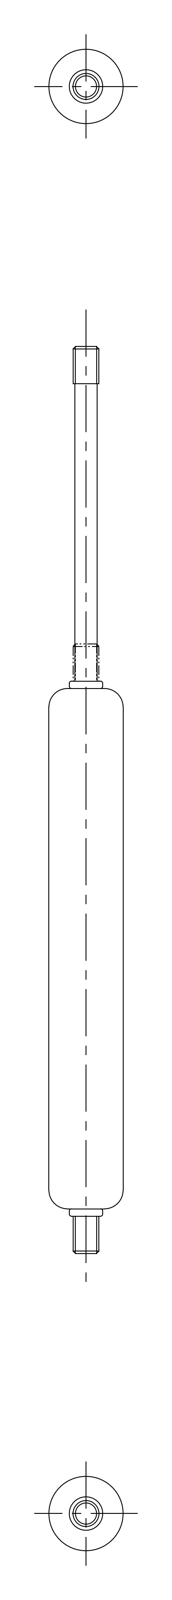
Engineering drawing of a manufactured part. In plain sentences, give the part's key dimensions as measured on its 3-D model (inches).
The part is named "rod; TM_277_40_80_29277_36". Its 3-D file was written by "CADfix (AUTOMOTIVE_DESIGN)". It is 2 solids with 36 faces: 0 planar, 0 cylindrical and 36 other. Overall it measures 4.803 by 0.394 by 0.394 inches. Its volume is 0.357 cubic inches and its surface area 4.391 square inches.
